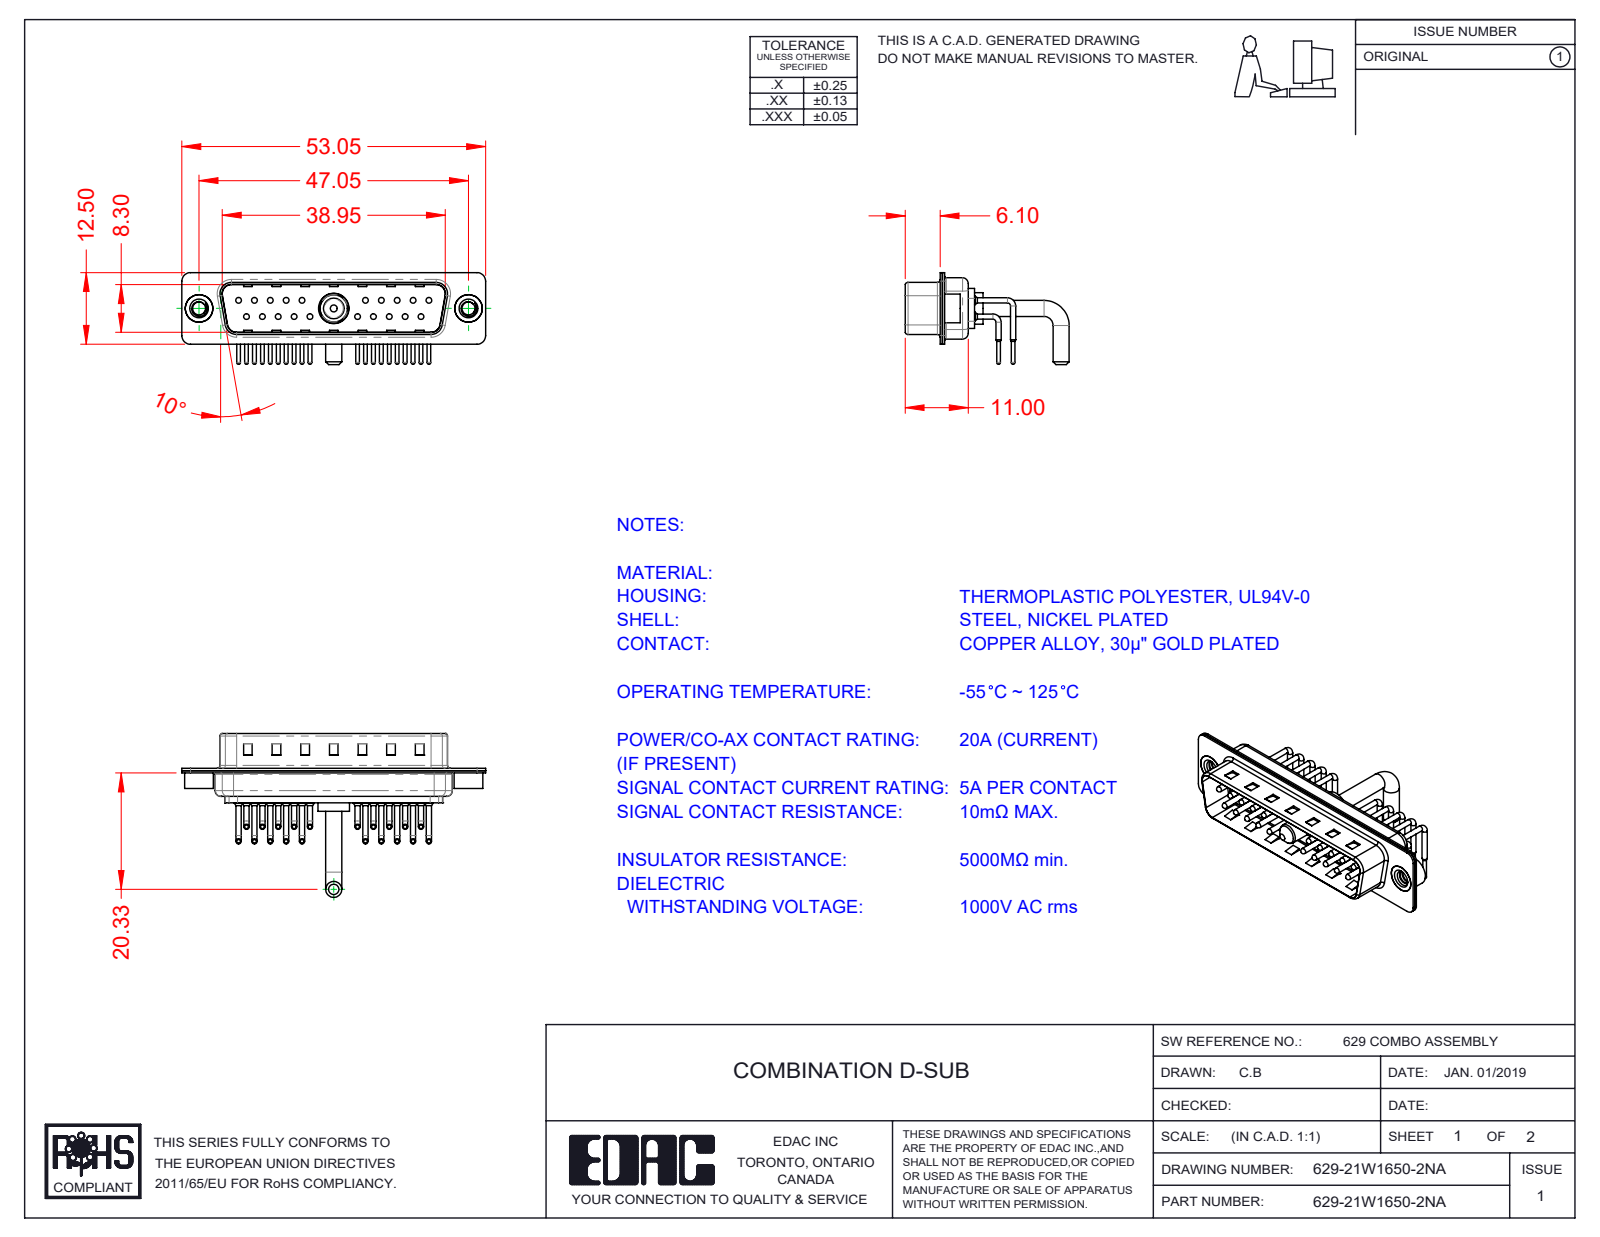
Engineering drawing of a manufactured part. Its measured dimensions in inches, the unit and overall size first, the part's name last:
Units: inches
Overall size (bounding box): 2.089 × 1.127 × 0.632
Round holes (diameter × count): ⌀0.03 ×20, ⌀0.063 ×20, ⌀0.079 ×20, ⌀0.089 ×2, ⌀0.157 ×2, ⌀0.189 ×2, ⌀0.191 ×1, ⌀0.209 ×1
Round bosses / shafts (diameter × count): ⌀0.035 ×40, ⌀0.059 ×20, ⌀0.039 ×20, ⌀0.026 ×20, ⌀0.197 ×2, ⌀0.193 ×2, ⌀0.11 ×2, ⌀0.217 ×1
Partial cylindrical surfaces — rounded edges, fillets, slot ends (radius × count): R0.04 ×20, R0.059 ×16, R0.079 ×12, R0.02 ×8, R0.063 ×8, R0.01 ×4, R0.024 ×4, R0.026 ×4
Main face-to-face distances: 0.016, 0.031, 0.374, 0.358, 0.343, 0.39, 0.03, 0.047, 0.22, 0.014
Hole centre spacings: 0.124, 0.109, 0.218, 0.327, 0.198, 0.763, 0.826, 0.872
Volume: 0.187 in³ · Surface area: 11.87 in²
Bodies: 27 solids, 2619 faces (1461 planar, 878 cylindrical, 280 other)
Part name (STEP PRODUCT): 629-21W1650-2NA; 629Combo Housing_21W1; 629Combo Contact Row 1; Power Pin_Ext 20A RA (+4 more)
STEP written by: SolidWorks 2020 (CONFIG_CONTROL_DESIGN)
